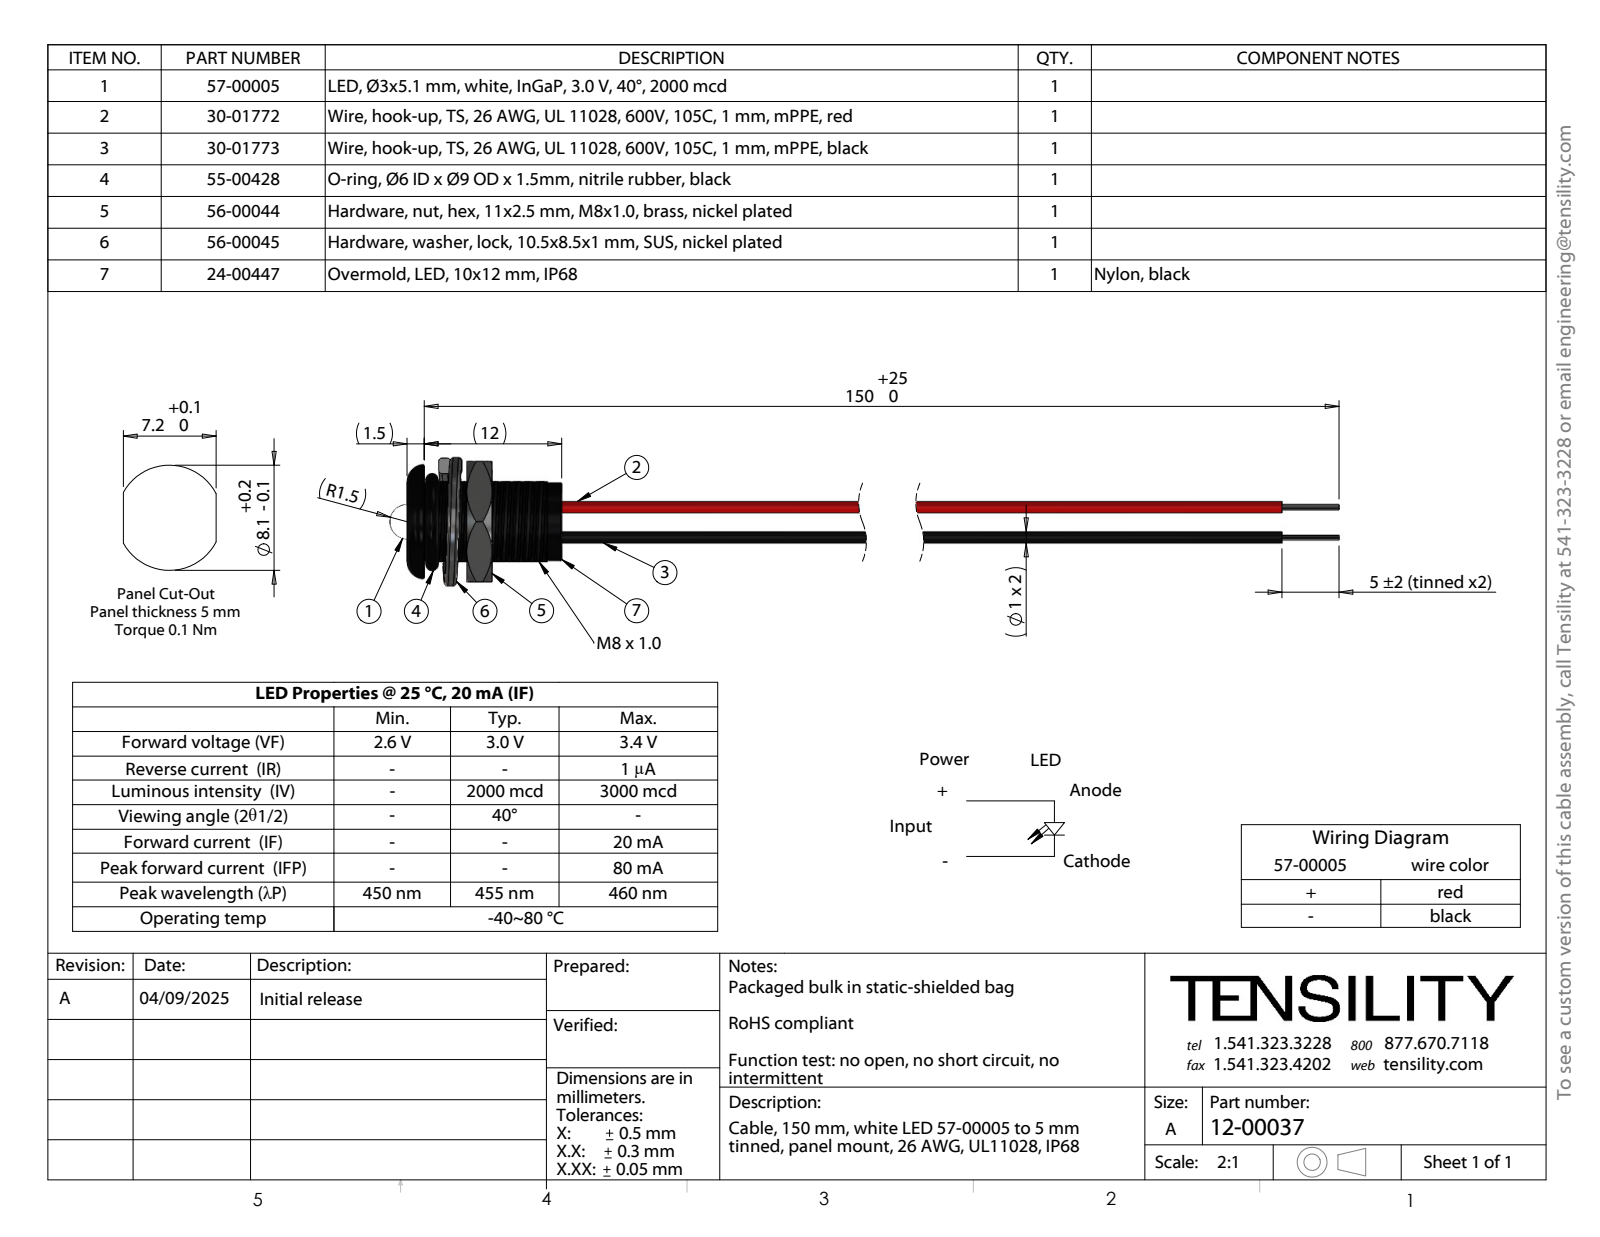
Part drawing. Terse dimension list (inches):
name: 12-00037; 30-01772_stripped and tinned; 57-00005_trimmed leads; 24-00447 (+4 more)
written by: SolidWorks 2021 (CONFIG_CONTROL_DESIGN)
unit: in
bodies: 57 solids, 555 faces (186 planar, 246 cylindrical, 123 other)
size: 6.693 × 0.477 × 0.441
volume: 0.061 in³; area: 9.157 in²
holes: 2× ⌀0.039
bosses: 2× ⌀0.039, 2× ⌀0.02, 1× ⌀0.268, 1× ⌀0.118
rounds: 1× R0.137, 1× R0.157
face distances: 0.059, 0.531, 0.472, 0.413, 0.205, 0.146, 0.326, 0.292, 0.233, 0.087
hole spacings: 0.014, 0.015, 0.013, 0.098, 0.099, 0.096, 0.096, 0.101
